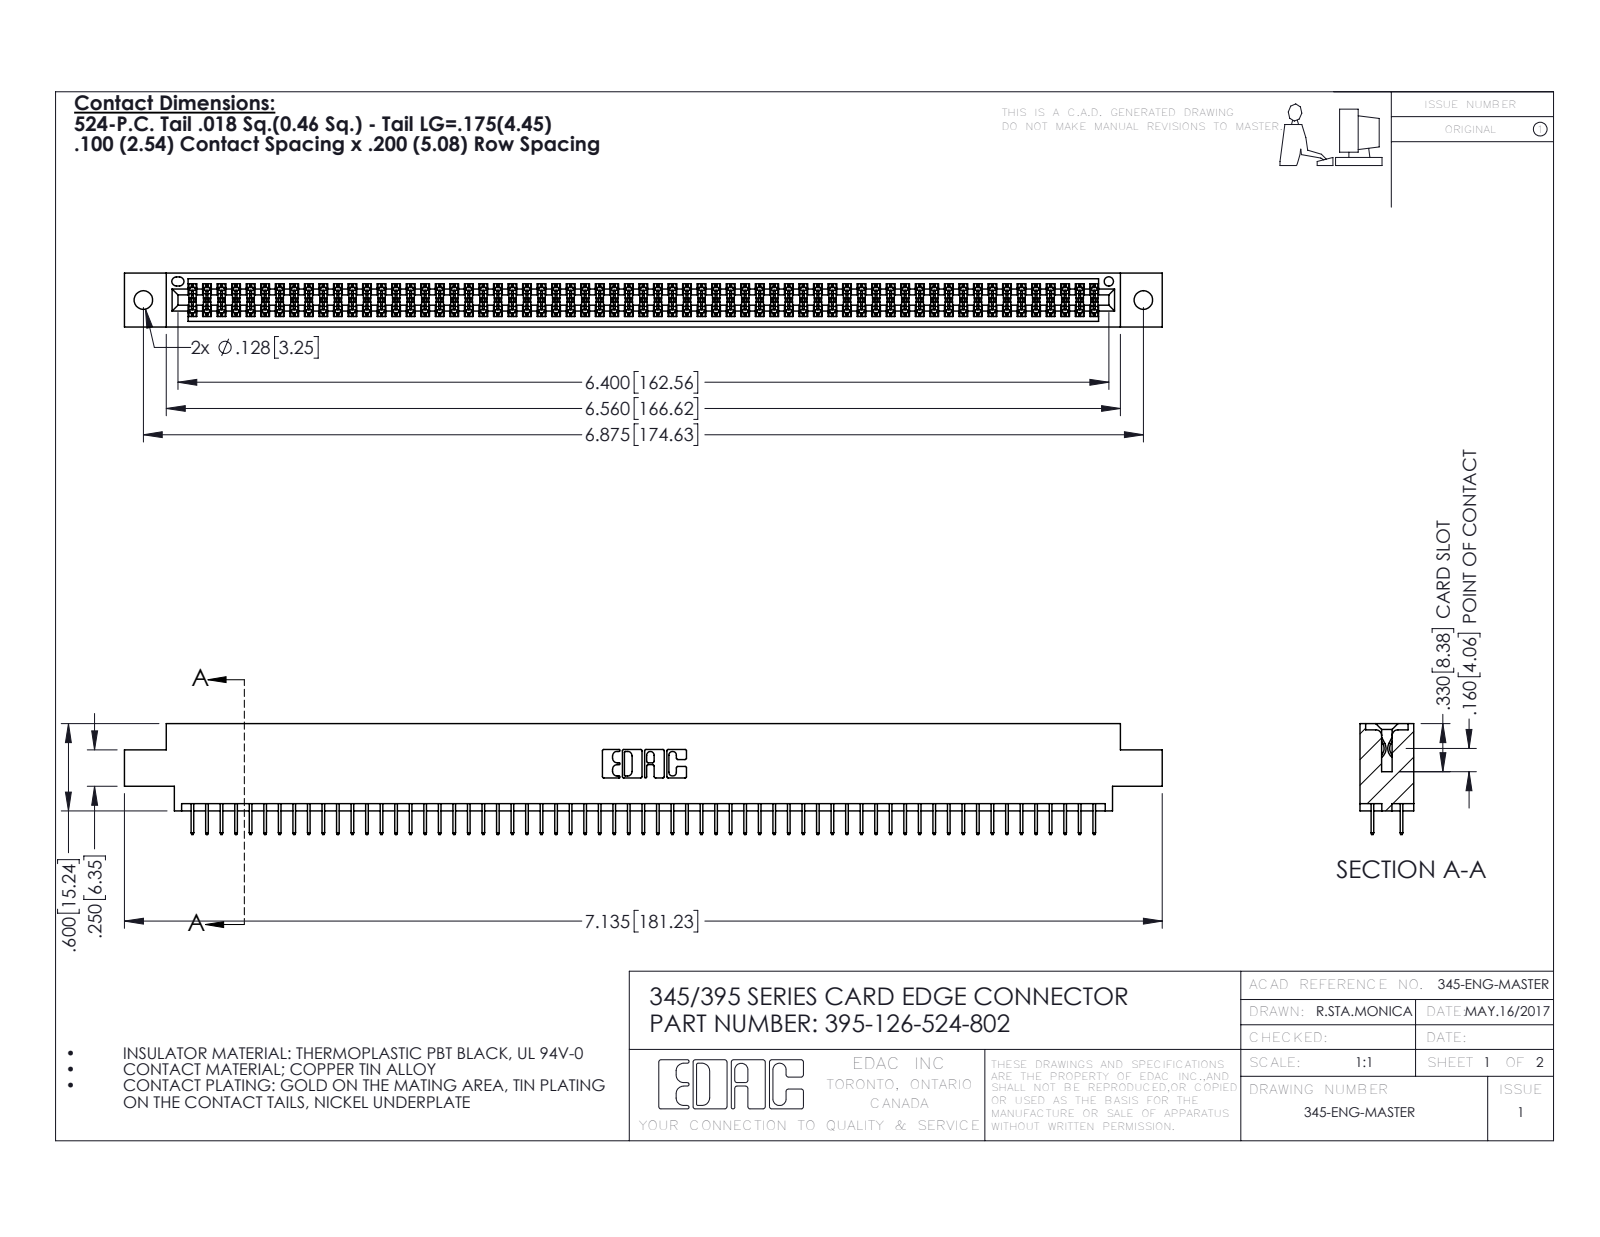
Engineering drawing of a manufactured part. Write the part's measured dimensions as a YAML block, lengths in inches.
part_name: "345-292-001_345-293-124; 395-126-524-802; 345 Part_0.170 Offset - 0.128 Dia"
step_written_by: "SolidWorks 2016 (CONFIG_CONTROL_DESIGN)"
units: inches
bodies: {solids: 127, faces: 6934, planar: 4998, cylindrical: 1936, other: 0}
overall_size: [7.135, 0.762, 0.37]
volume: 1.065
surface_area: 39.65
round_holes:
  - {diameter: 0.128, count: 2}
  - {diameter: 0.064, count: 1}
partial_cylinders:
  - {radius: 0.006, count: 189}
  - {radius: 0.01, count: 22}
  - {radius: 0.007, count: 6}
  - {radius: 0.031, count: 6}
  - {radius: 0.026, count: 3}
  - {radius: 0.014, count: 2}
  - {radius: 0.019, count: 2}
  - {radius: 0.022, count: 2}
face_to_face_distances: [0.072, 0.298, 0.37, 0.2, 0.098, 0.272, 0.025, 0.225, 0.072, 0.175]
hole_center_spacings: [0.27, 6.639, 6.875]
